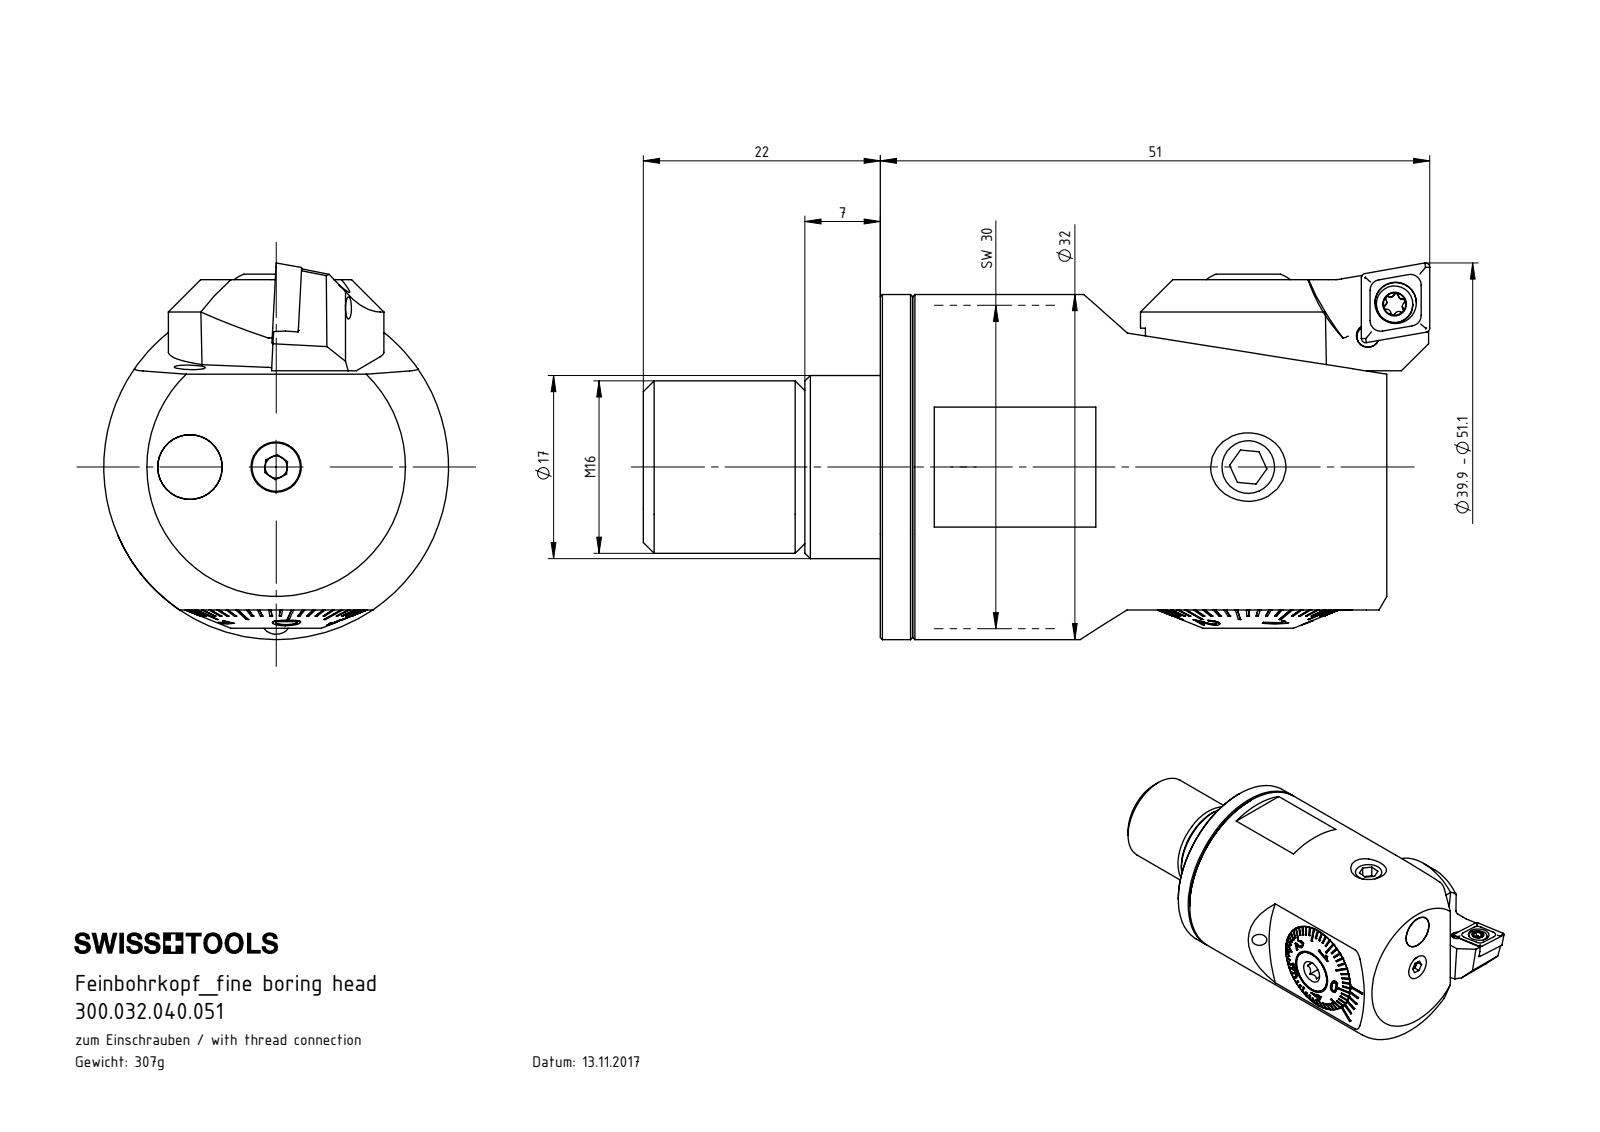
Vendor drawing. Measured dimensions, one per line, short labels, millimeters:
name: F32-BG3.006.026_A; F32-ER1.101.010_A; F32-WCA.001.007; 300.032.040.051 (+8 more)
written by: SolidWorks 2017 (CONFIG_CONTROL_DESIGN)
unit: mm
bodies: 20 solids, 837 faces (363 planar, 158 cylindrical, 316 other)
size: 73 × 34.94 × 32
volume: 39 272 mm³; area: 20 275 mm²
holes: 5× ⌀2.5, 2× ⌀5, 2× ⌀17, 1× ⌀2, 1× ⌀2.05, 1× ⌀2.1, 1× ⌀2.7, 1× ⌀2.8, 1× ⌀2.9, 1× ⌀3, 1× ⌀3.3, 1× ⌀3.85
bosses: 2× ⌀6, 2× ⌀2.5, 1× ⌀32, 1× ⌀16.98, 1× ⌀16.85, 1× ⌀16, 1× ⌀14.65, 1× ⌀12
rounds: 6× R0.21, 5× R0.36, 4× R0.5, 2× R1.75, 1× R0.36, 1× R1, 1× R1.07, 1× R1.9
face distances: 3, 47, 44, 4.5, 25.14, 30, 8, 0.8, 1.5, 3.7
hole spacings: 3.84, 3.99, 5.7, 8, 11.68, 24.15
